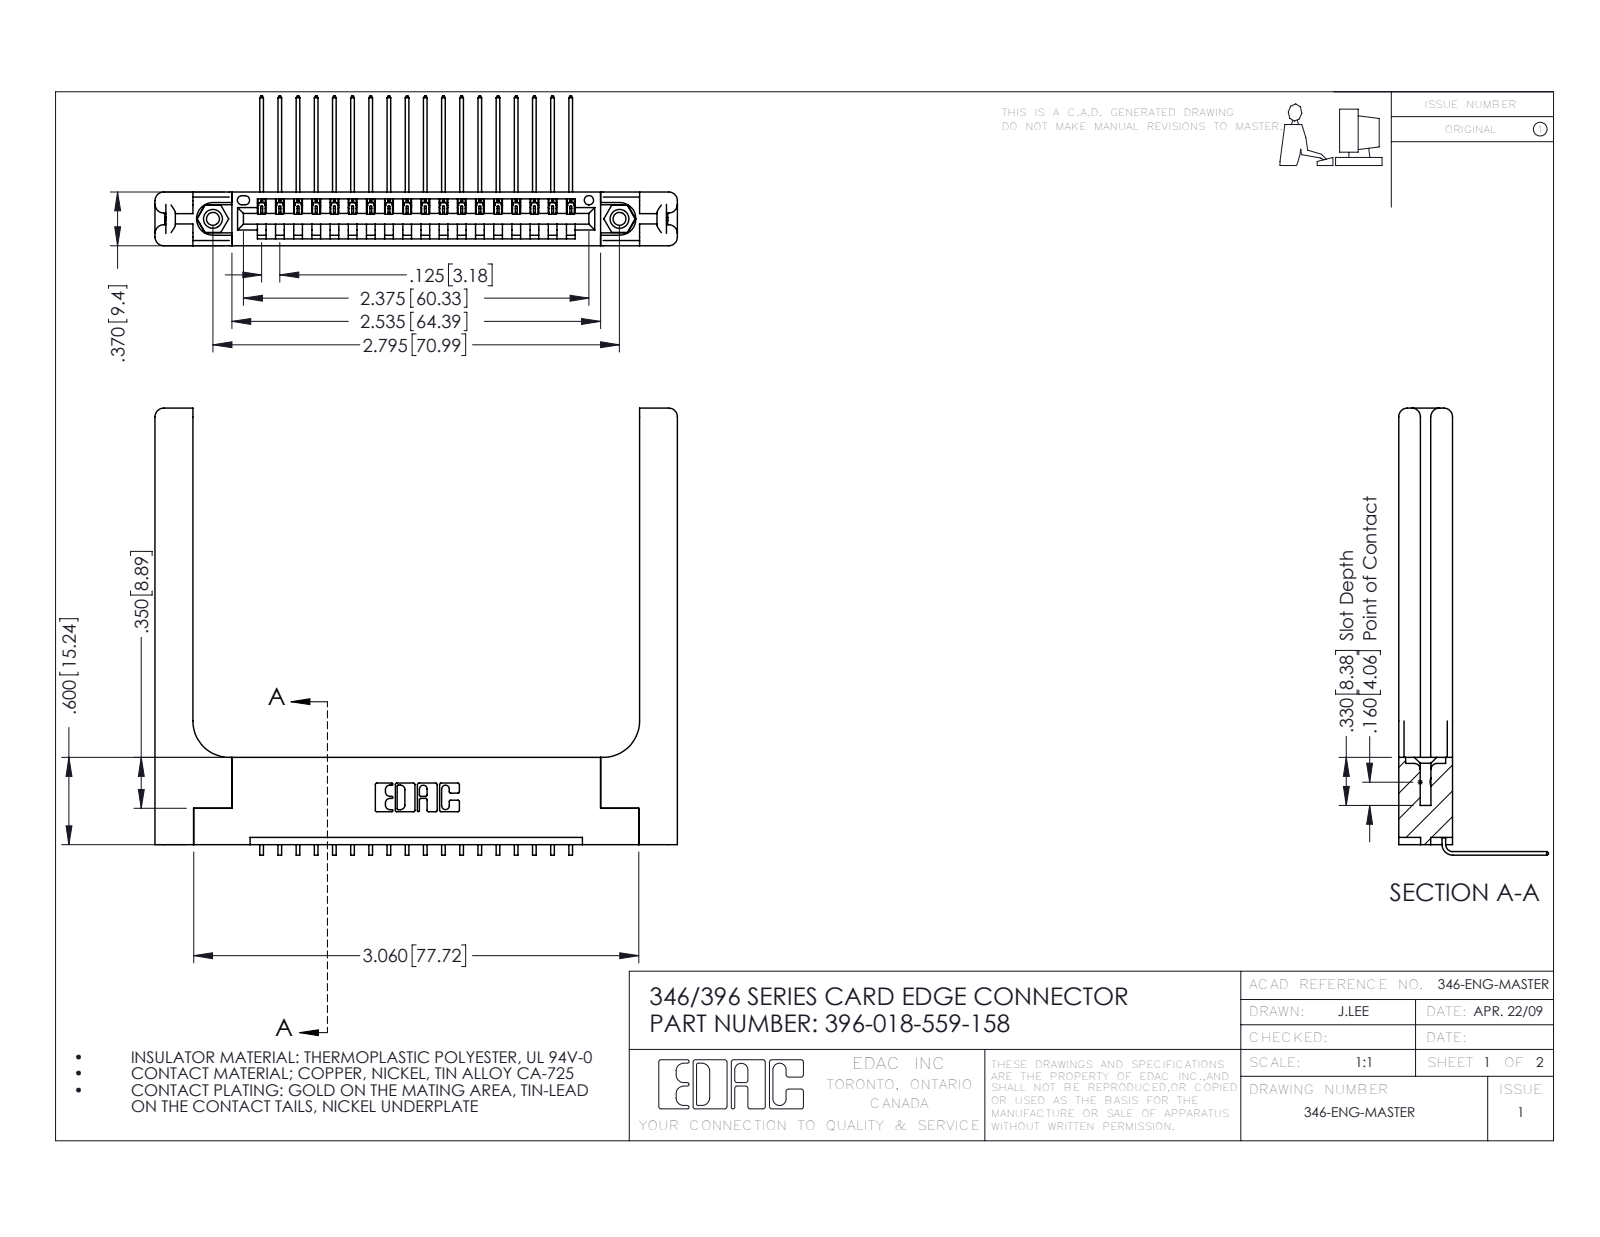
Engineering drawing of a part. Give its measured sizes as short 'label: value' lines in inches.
name: 346-220-058_345-220-058; 396-018-559-158; 345-292-001_558 559 Tail - 1; 345-250-001_345-250-001-102 (+1 more)
written by: SolidWorks 2016 (CONFIG_CONTROL_DESIGN)
unit: in
bodies: 23 solids, 1458 faces (980 planar, 418 cylindrical, 60 other)
size: 3.591 × 3.073 × 1.03
volume: 0.985 in³; area: 24.88 in²
holes: 2× ⌀0.089, 2× ⌀0.125, 2× ⌀0.156, 1× ⌀0.064
bosses: 2× ⌀0.155
rounds: 36× R0.006, 22× R0.01, 16× R0.06, 6× R0.007, 6× R0.031, 3× R0.026, 2× R0.03, 2× R0.031
face distances: 0.37, 0.072, 0.15, 0.322, 0.048, 0.148, 0.25, 0.298, 0.025, 0.102
hole spacings: 0.246, 2.588, 2.795
